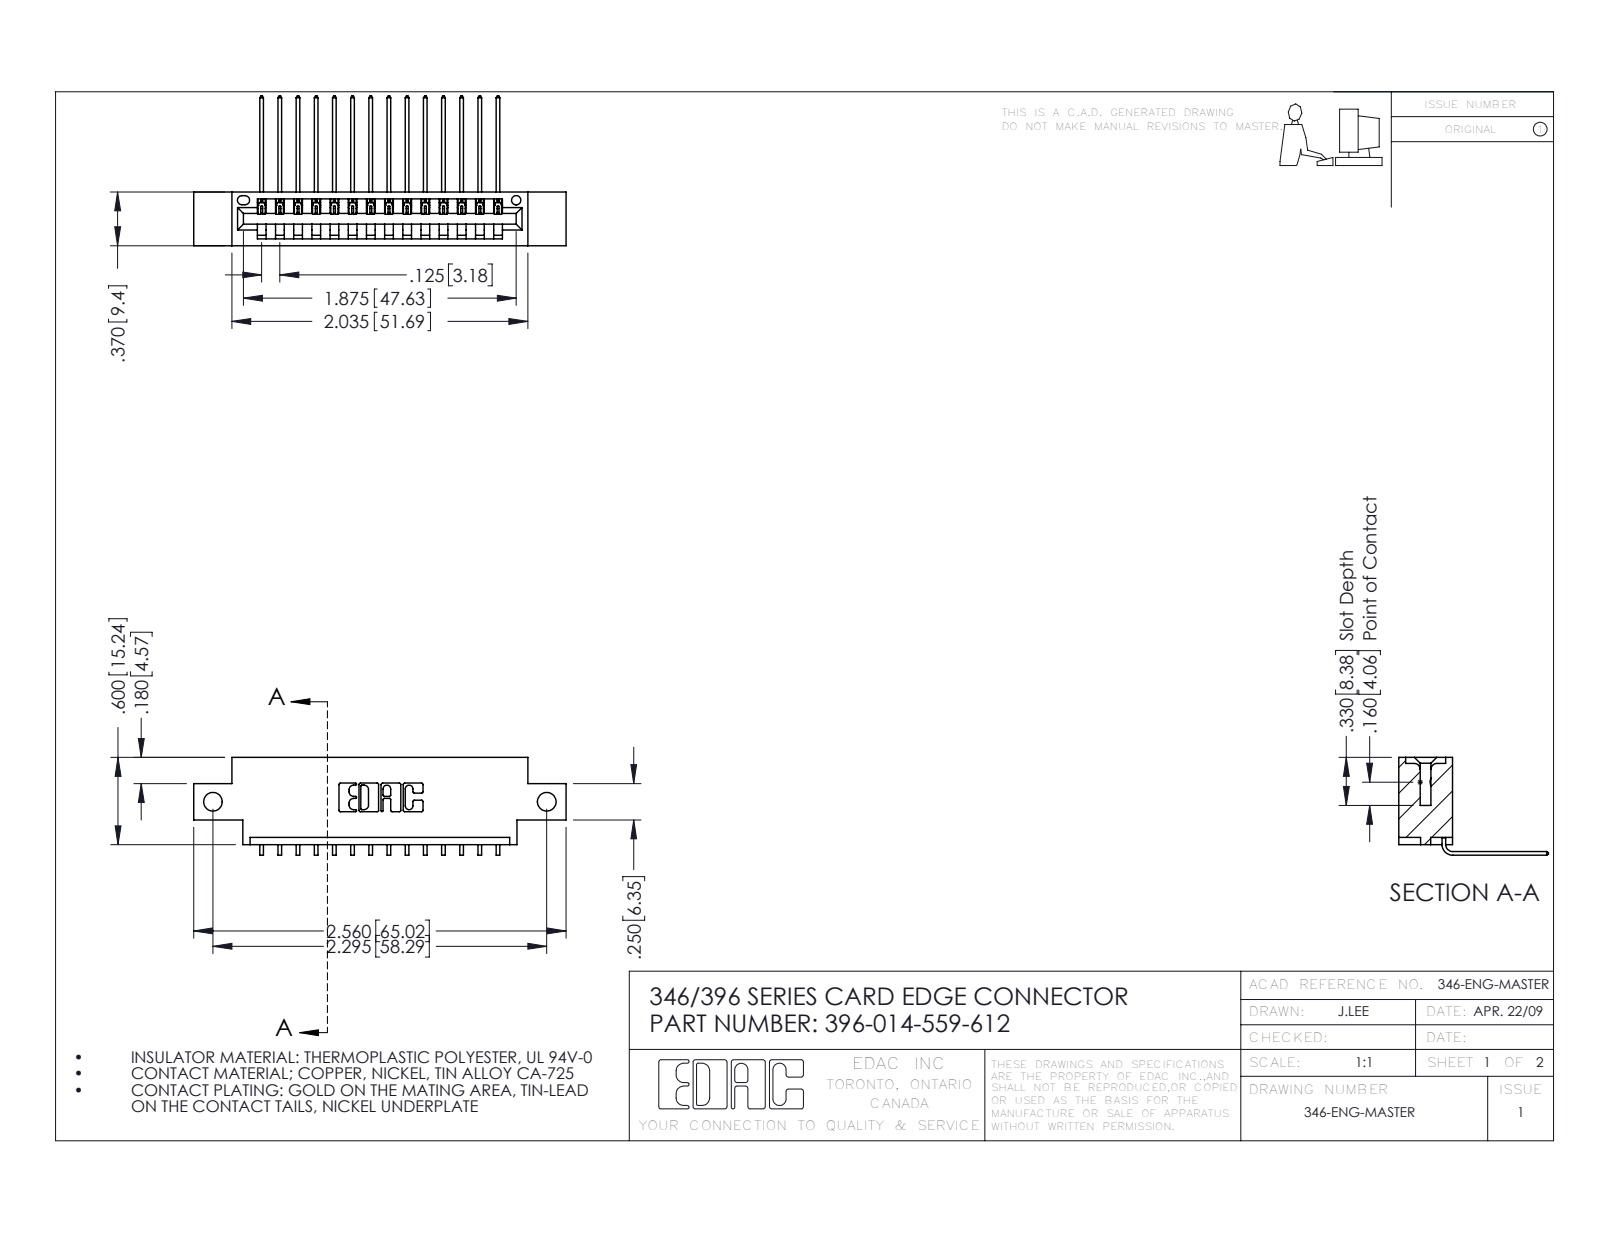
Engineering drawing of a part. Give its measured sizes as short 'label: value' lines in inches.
name: 346 Part_0.170 Offset - Side Mount; 396-014-559-612; 345-292-001_558 559 Tail - 1
written by: SolidWorks 2016 (CONFIG_CONTROL_DESIGN)
unit: in
bodies: 15 solids, 966 faces (668 planar, 298 cylindrical, 0 other)
size: 2.56 × 1.03 × 0.673
volume: 0.356 in³; area: 11.29 in²
holes: 2× ⌀0.128, 1× ⌀0.064
rounds: 28× R0.006, 22× R0.01, 6× R0.007, 6× R0.031, 3× R0.026, 2× R0.031, 2× R0.04, 1× R0.014
face distances: 0.048, 0.37, 0.322, 0.25, 0.025, 0.072, 0.148, 0.222, 0.1, 0.174
hole spacings: 2.295
